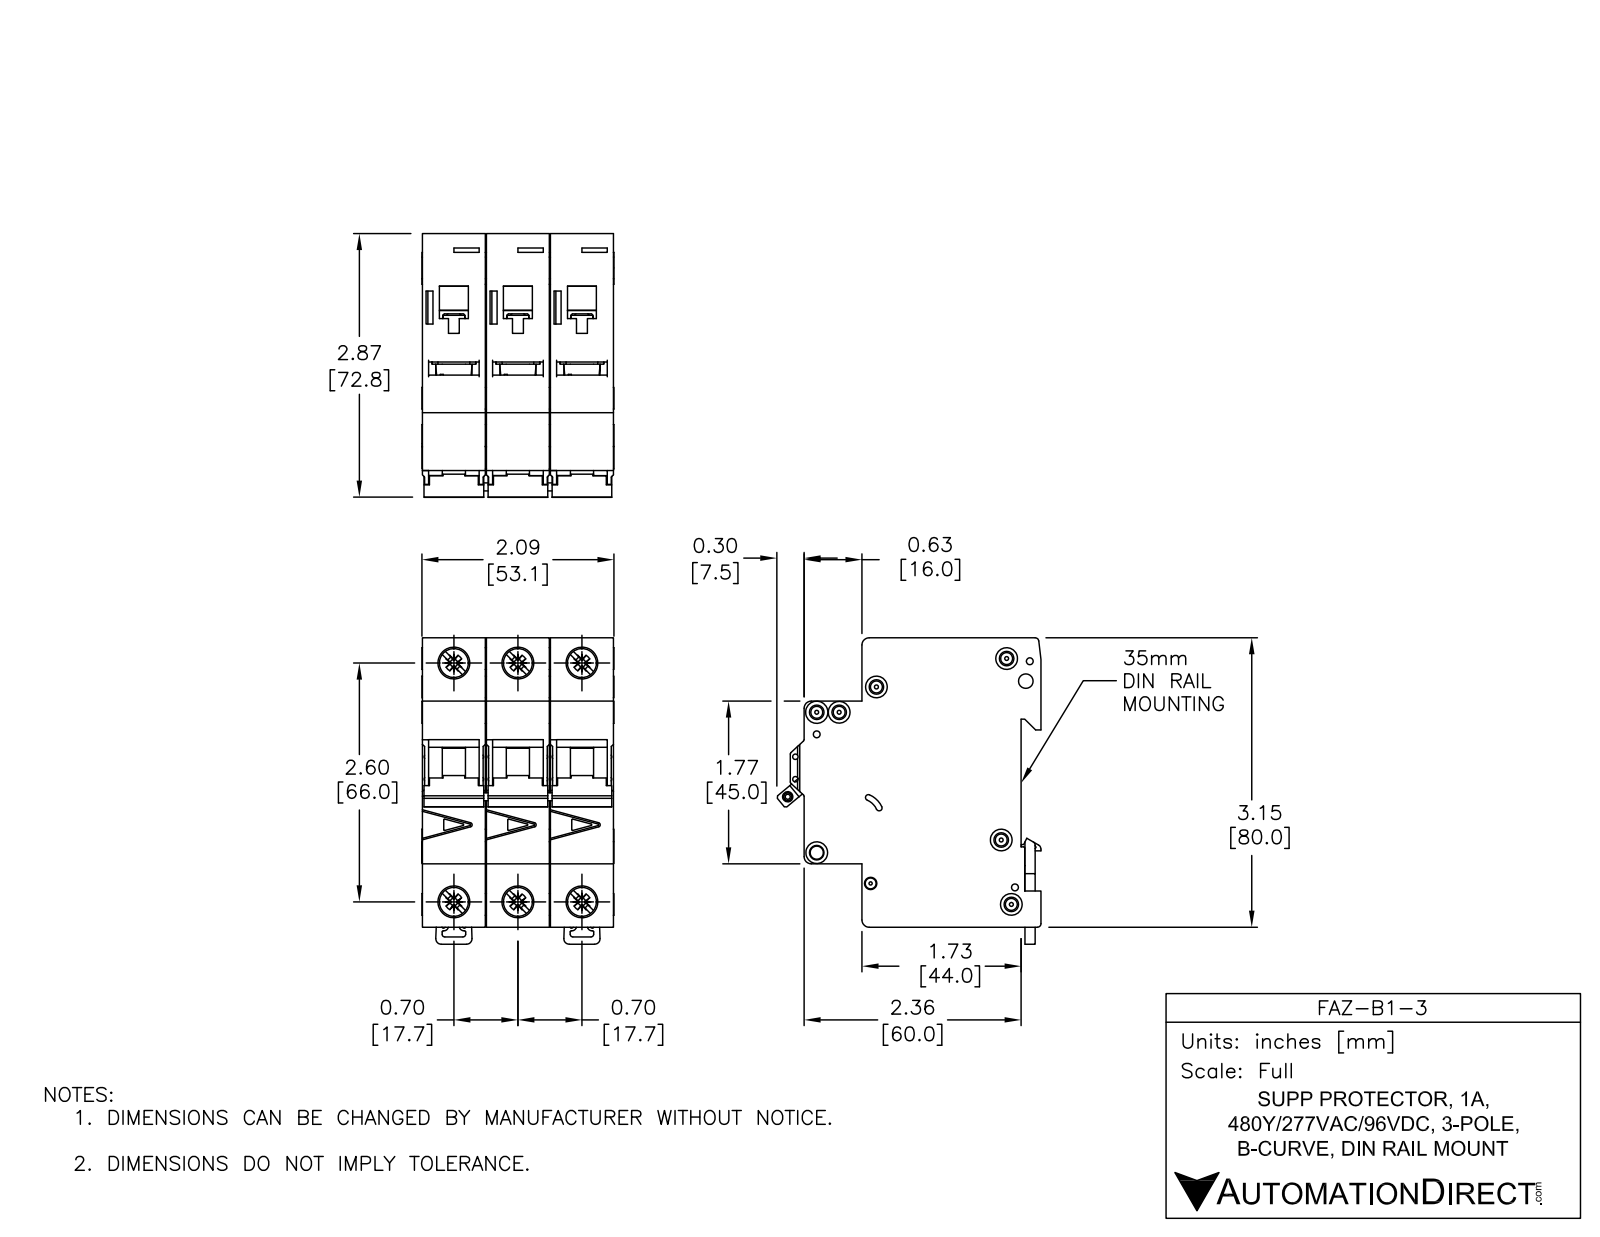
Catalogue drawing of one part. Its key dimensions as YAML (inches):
part_name: "FAZ-B1-3"
step_written_by: "SolidWorks 2014 (AUTOMOTIVE_DESIGN)"
units: inches
bodies: {solids: 11, faces: 1650, planar: 697, cylindrical: 590, other: 363}
overall_size: [3.338, 2.876, 2.091]
volume: 13.71
surface_area: 89.98
round_holes:
  - {diameter: 0.142, count: 6}
  - {diameter: 0.323, count: 4}
  - {diameter: 0.075, count: 3}
  - {diameter: 0.043, count: 2}
  - {diameter: 0.059, count: 2}
  - {diameter: 0.157, count: 2}
  - {diameter: 0.281, count: 2}
  - {diameter: 0.085, count: 1}
  - {diameter: 0.087, count: 1}
  - {diameter: 0.1, count: 1}
  - {diameter: 0.13, count: 1}
  - {diameter: 0.134, count: 1}
round_bosses_or_shafts:
  - {diameter: 0.236, count: 4}
  - {diameter: 0.098, count: 3}
  - {diameter: 0.323, count: 2}
partial_cylinders:
  - {radius: 0.01, count: 68}
  - {radius: 0.02, count: 25}
  - {radius: 0.039, count: 12}
  - {radius: 0.079, count: 12}
  - {radius: 0.008, count: 11}
  - {radius: 0.071, count: 3}
  - {radius: 0.031, count: 2}
  - {radius: 0.118, count: 2}
face_to_face_distances: [0.697, 0.689, 1.394, 1.386, 2.083, 0.705, 3.129, 0.217, 1.949, 1.732]
hole_center_spacings: [0.697, 2.69, 2.598, 0.244, 0.537, 1.394, 2.948, 0.189]
